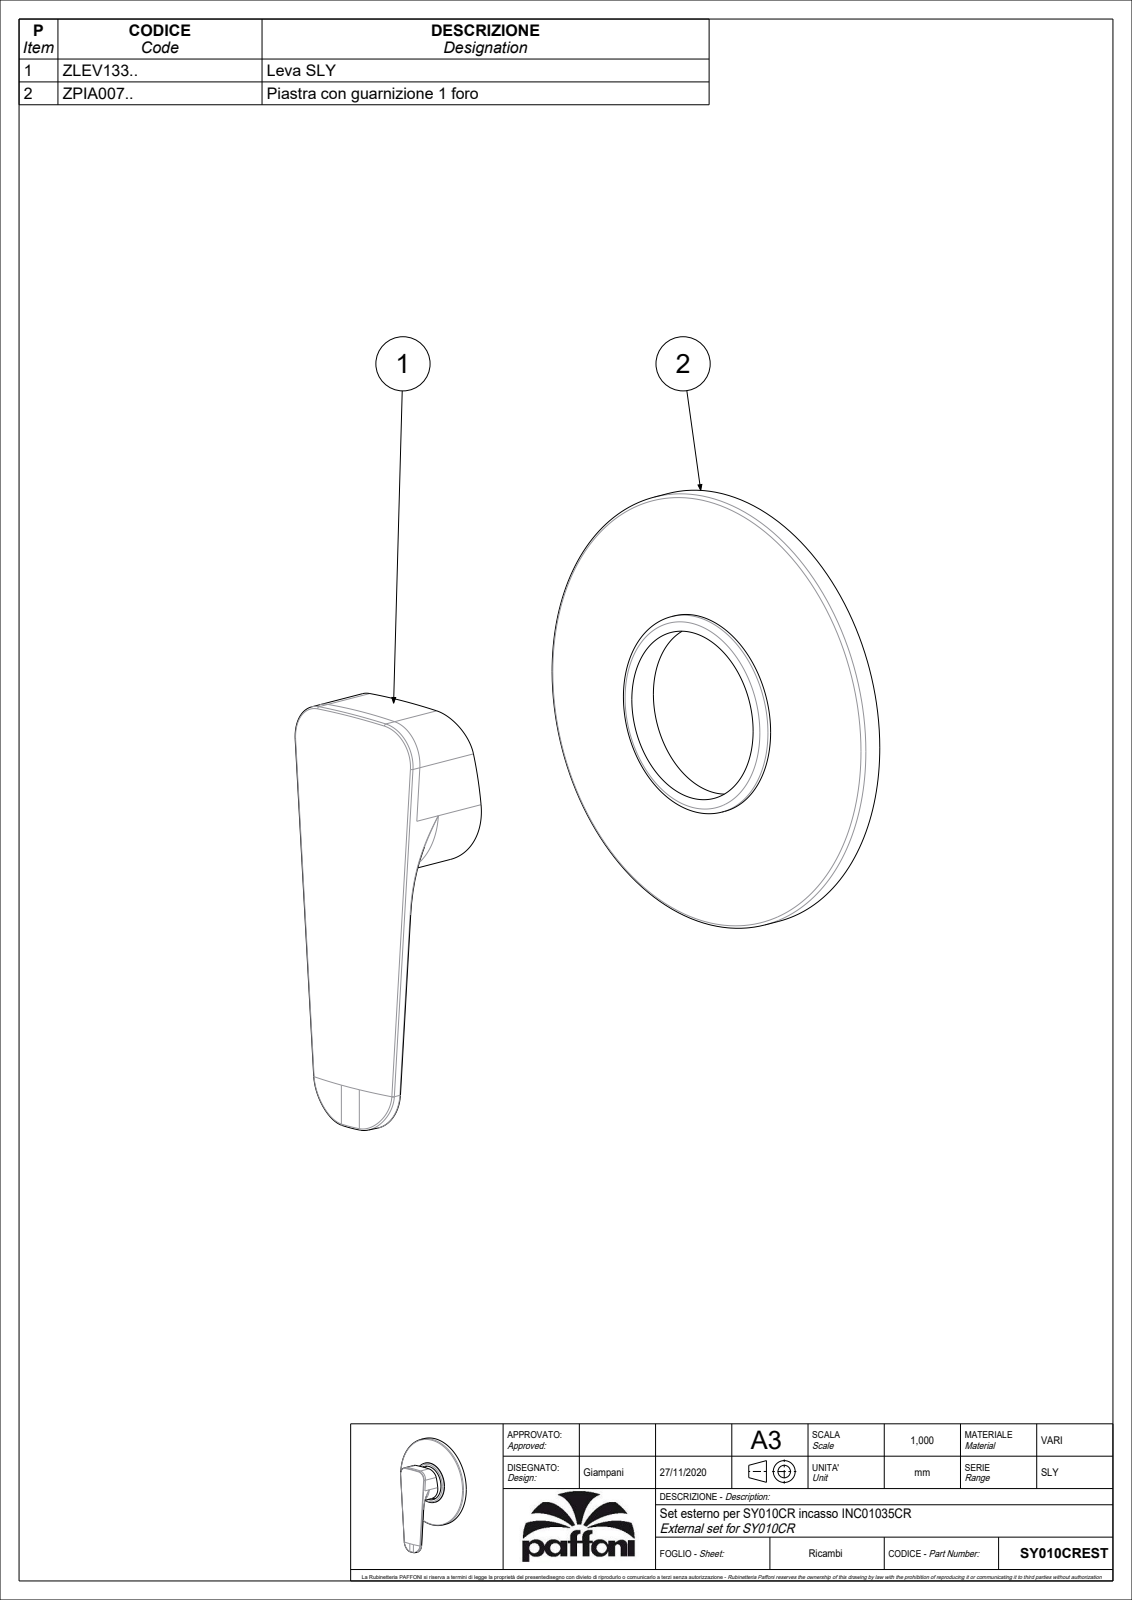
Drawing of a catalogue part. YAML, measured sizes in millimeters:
part_name: "SY010CREST"
step_written_by: "CREO PARAMETRIC BY PTC INC, 2020044 (CONFIG_CONTROL_DESIGN)"
units: millimeters
bodies: {solids: 2, faces: 165, planar: 47, cylindrical: 48, other: 70}
overall_size: [146.18, 116, 43.5]
volume: 35000
surface_area: 41670
round_holes:
  - {diameter: 3, count: 1}
  - {diameter: 3.3, count: 1}
  - {diameter: 4.5, count: 1}
  - {diameter: 45, count: 1}
  - {diameter: 50, count: 1}
  - {diameter: 114, count: 1}
round_bosses_or_shafts:
  - {diameter: 116, count: 1}
  - {diameter: 53, count: 1}
  - {diameter: 7.6, count: 1}
  - {diameter: 5.5, count: 1}
  - {diameter: 5, count: 1}
partial_cylinders:
  - {radius: 1.5, count: 4}
  - {radius: 10, count: 2}
  - {radius: 4.5, count: 1}
  - {radius: 20.68, count: 1}
  - {radius: 112.27, count: 1}
  - {radius: 200, count: 1}
face_to_face_distances: [4, 27.5, 11.5, 39, 9, 3.5, 7.5, 5.5, 1.5, 2.5]
